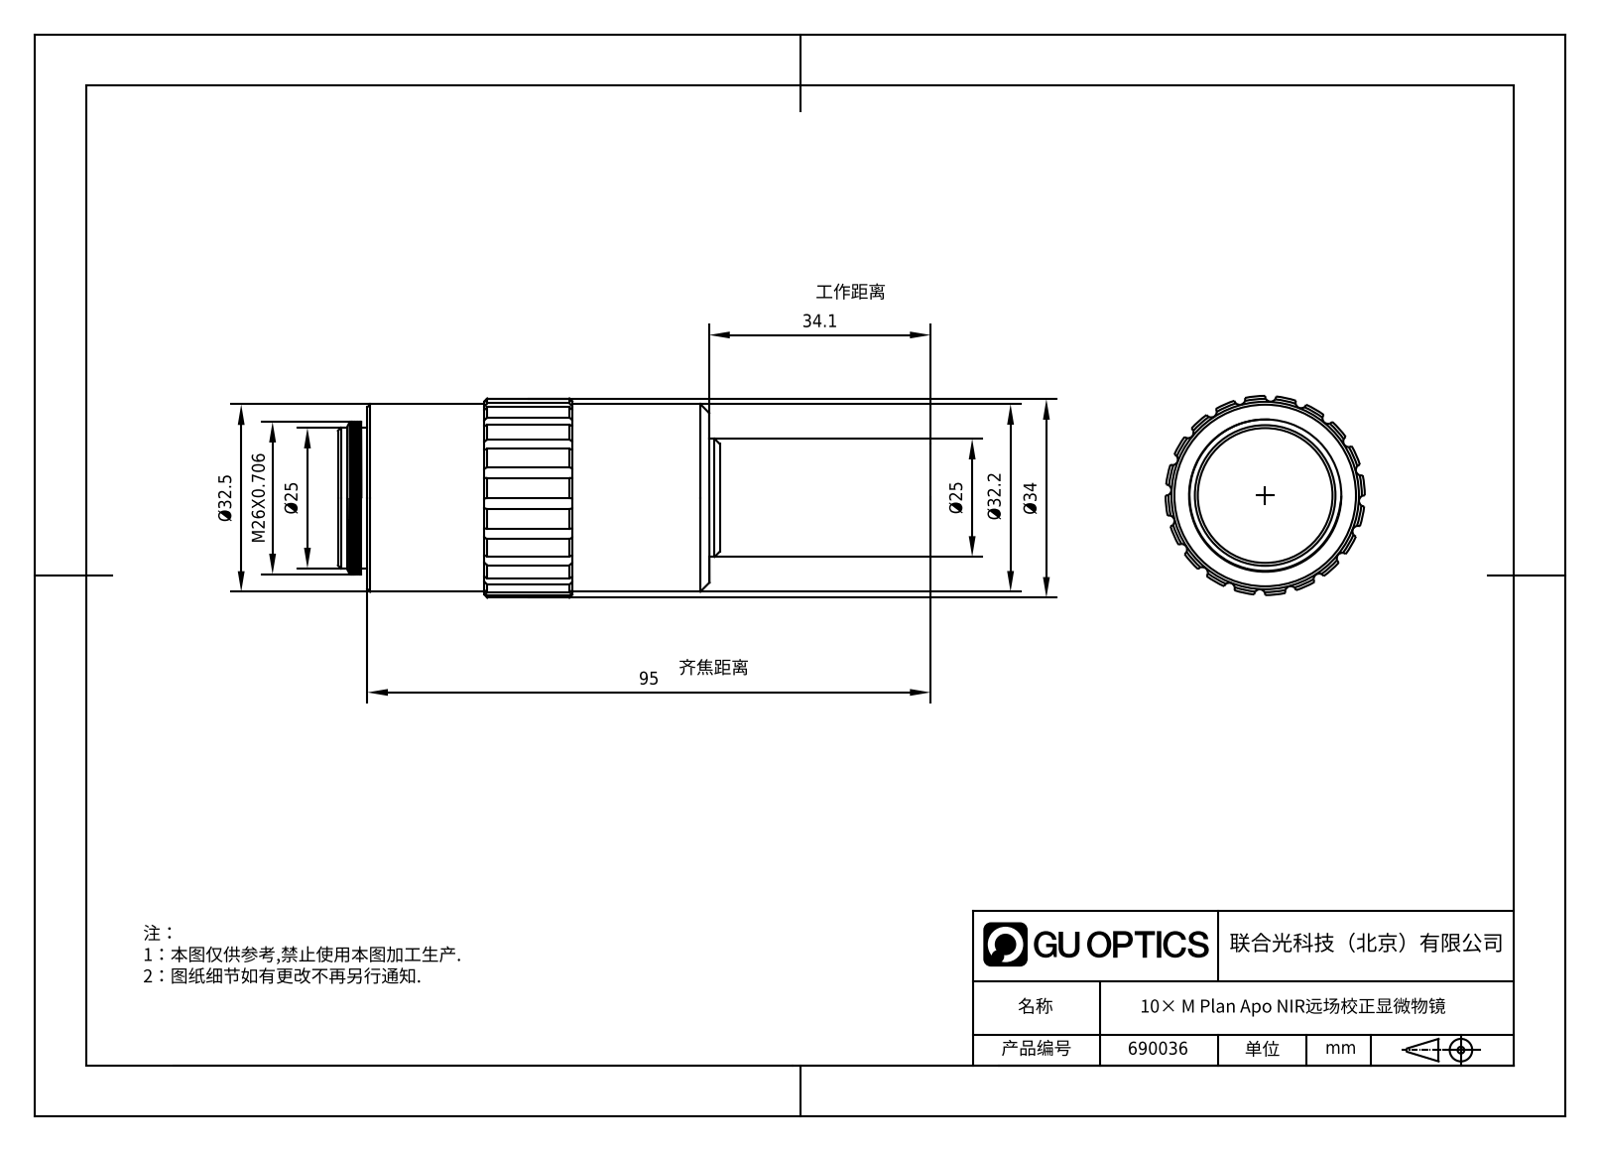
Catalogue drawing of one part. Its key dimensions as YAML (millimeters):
part_name: "690036"
step_written_by: "SolidWorks 2020 (CONFIG_CONTROL_DESIGN)"
units: millimeters
bodies: {solids: 3, faces: 316, planar: 13, cylindrical: 81, other: 222}
overall_size: [85.96, 33.97, 33.97]
volume: 68265
surface_area: 14754
round_holes:
  - {diameter: 21.9, count: 1}
round_bosses_or_shafts:
  - {diameter: 32, count: 1}
  - {diameter: 26, count: 1}
  - {diameter: 25, count: 1}
  - {diameter: 24, count: 1}
partial_cylinders:
  - {radius: 0.71, count: 16}
  - {radius: 15.99, count: 1}
  - {radius: 17, count: 1}
face_to_face_distances: [83.11, 0.79, 83.9, 78.9, 78.11, 5, 0.5, 1.29, 79.4, 84.4]
